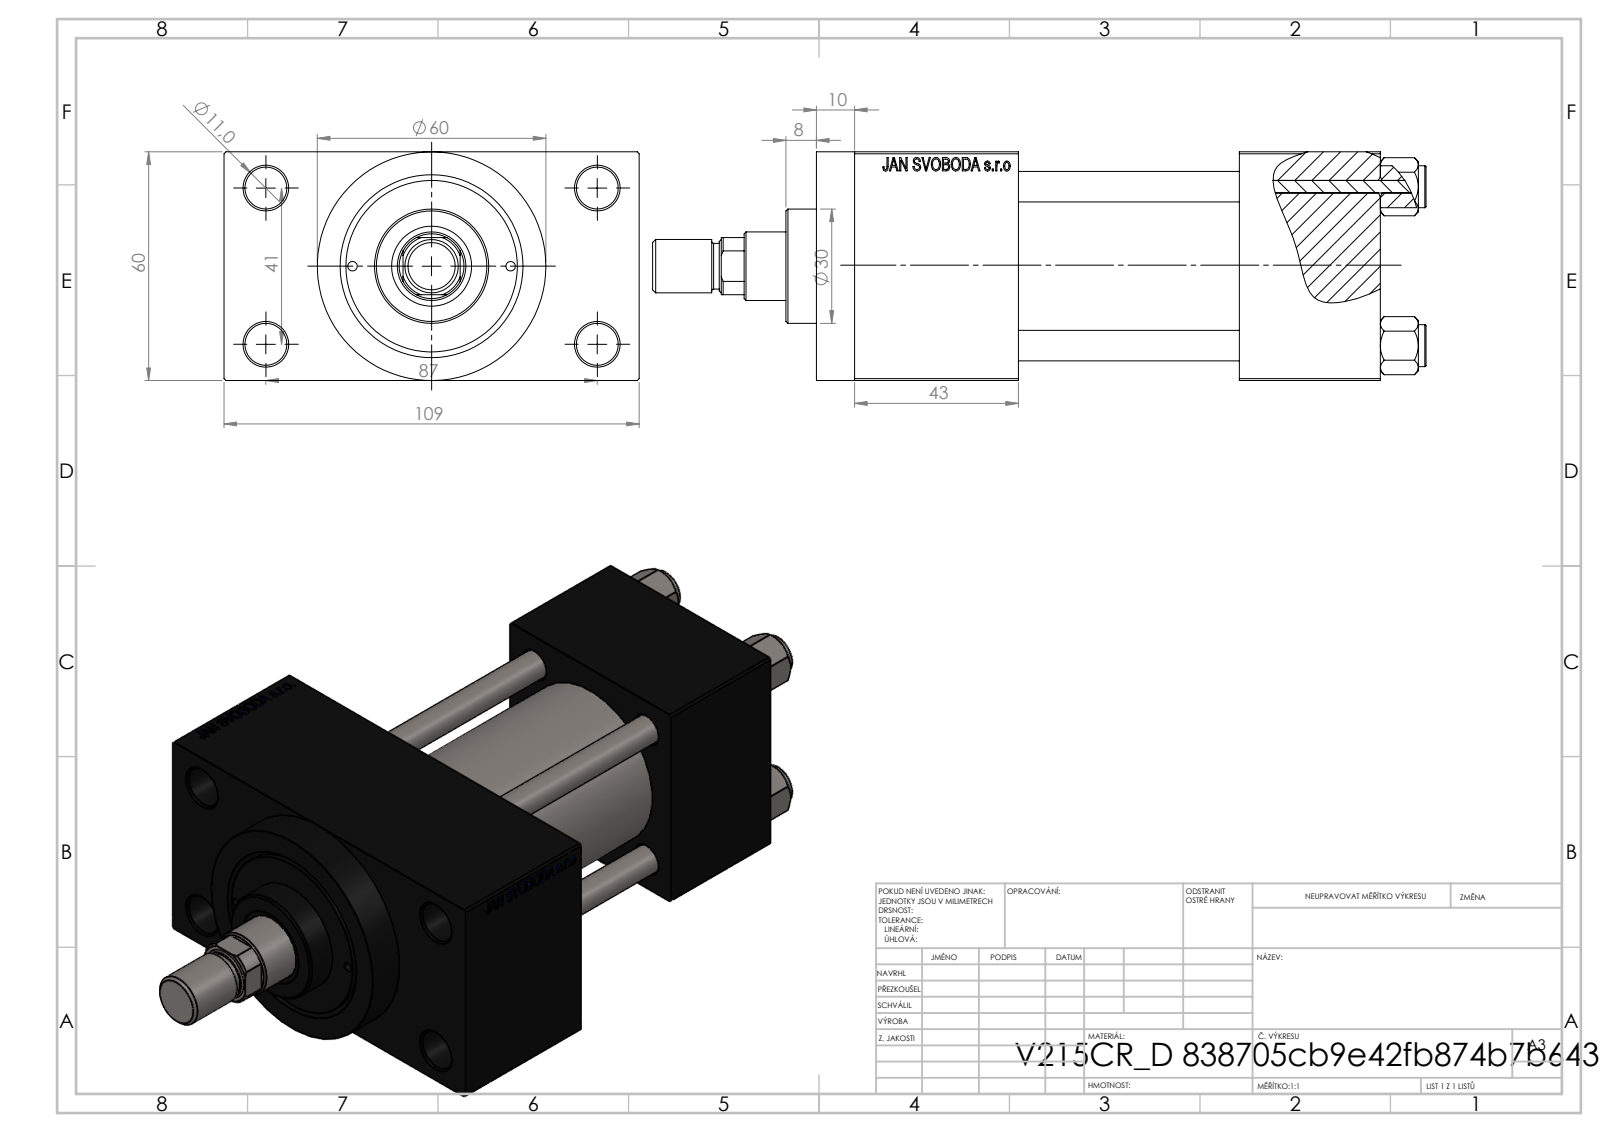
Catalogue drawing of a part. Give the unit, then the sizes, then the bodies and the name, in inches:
Units: inches
Overall size (bounding box): 7.992 × 4.291 × 2.362
Round holes (diameter × count): ⌀0.315 ×4, ⌀0.433 ×4, ⌀0.098 ×2, ⌀0.276 ×2, ⌀0.656 ×2, ⌀0.945 ×2, ⌀0.335 ×1, ⌀0.709 ×1, ⌀0.827 ×1, ⌀1.22 ×1, ⌀1.575 ×1, ⌀1.772 ×1
Round bosses / shafts (diameter × count): ⌀0.433 ×4, ⌀2.362 ×1, ⌀1.811 ×1, ⌀1.181 ×1, ⌀0.551 ×1, ⌀0.472 ×1
Partial cylindrical surfaces — rounded edges, fillets, slot ends (radius × count): R0.335 ×1
Main face-to-face distances: 2.362, 2.283, 0.965, 3.327, 1.457, 3.74, 1.693, 5.433, 3.976, 4.124
Hole centre spacings: 0.821, 0.892, 1.161, 1.206, 1.642, 1.832, 1.856, 1.893
Volume: 31.43 in³ · Surface area: 191.6 in²
Bodies: 12 solids, 1126 faces (504 planar, 96 cylindrical, 526 other)
Part name (STEP PRODUCT): NUT_M5_D; V215CR_D_TYCINKA; ROD_END_AH; V215_VC_A (+2 more)
STEP written by: SolidWorks 2019 (CONFIG_CONTROL_DESIGN)
